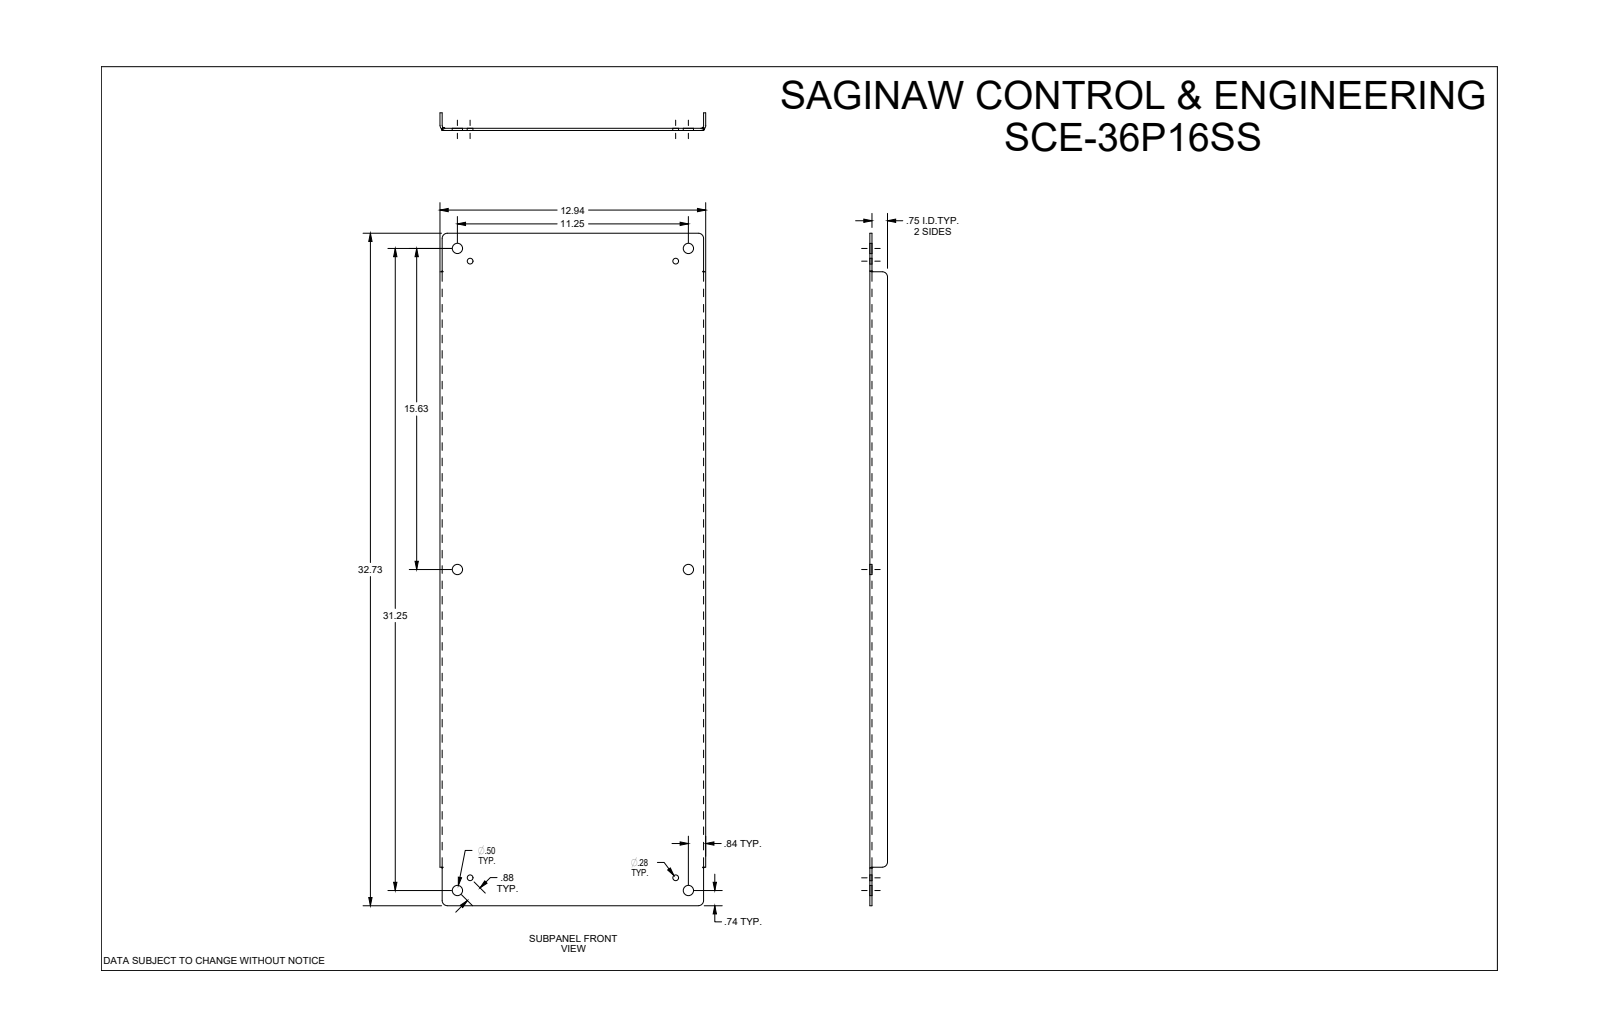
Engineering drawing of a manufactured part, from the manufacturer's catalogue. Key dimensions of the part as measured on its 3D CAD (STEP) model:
Part name (STEP PRODUCT): SCE-36P16SS
STEP written by: SolidWorks 2019 (CONFIG_CONTROL_DESIGN)
Units: inches
Bodies: 1 solid, 52 faces (18 planar, 22 cylindrical, 12 other)
Overall size (bounding box): 32.734 × 12.941 × 0.858
Volume: 47.86 in³ · Surface area: 931.4 in²
Round holes (diameter × count): ⌀0.5 ×6, ⌀0.281 ×4
Partial cylindrical surfaces — rounded edges, fillets, slot ends (radius × count): R0.25 ×6, R0.246 ×2, R0.142 ×1, R0.143 ×1
Main face-to-face distances: 0.104, 12.838, 12.734, 12.942, 0.754, 0.858, 32.734, 1.875, 30.859, 28.983
Hole centre spacings: 0.875, 10.651, 15.02, 15.627, 18.393, 19.256, 30.641, 32.428
